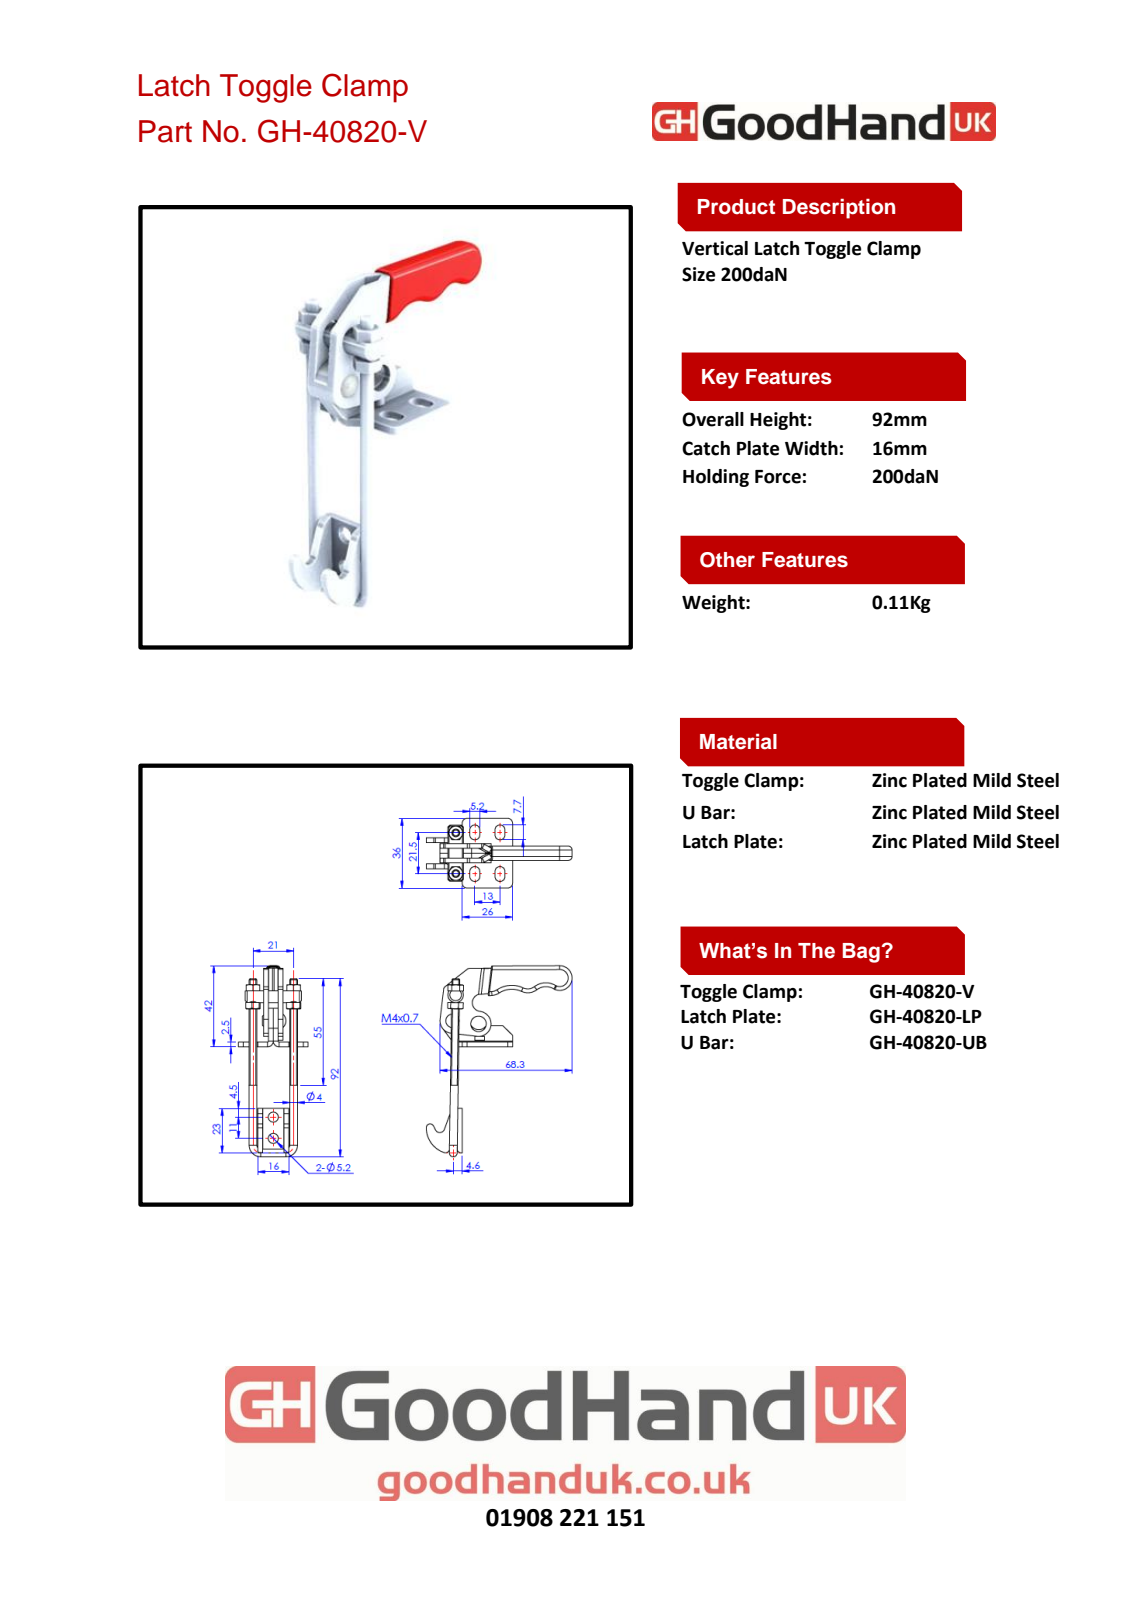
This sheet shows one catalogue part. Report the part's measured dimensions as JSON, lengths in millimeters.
{"part_name": "GH-40820-V(簡化); Group1^GH-40820(簡化); 44082044-1^GH-40820-V(簡化); 14082015-1-2^GH-40820-V(簡化) (+2 more)", "step_written_by": "SolidWorks 2016 (AUTOMOTIVE_DESIGN)", "units": "millimeters", "bodies": {"solids": 7, "faces": 429, "planar": 115, "cylindrical": 152, "other": 162}, "overall_size": [99.35, 75.37, 36], "volume_mm3": 16318, "surface_area_mm2": 13950, "round_holes": [[4, 4], [3.3, 2], [5.2, 2], [8, 2], [3, 1]], "round_bosses_or_shafts": [[4, 3]], "partial_cylinders_radius": [[2, 9], [2.5, 9], [0.5, 8], [2.6, 8], [3, 6], [4.5, 4], [0.1, 2], [6.5, 2]], "face_to_face_distances": [2.5, 7.5, 10.5, 5, 3, 10, 13, 0.5, 5.5, 13.5], "hole_center_spacings": [21, 11, 13.5, 13.51, 19.09]}
